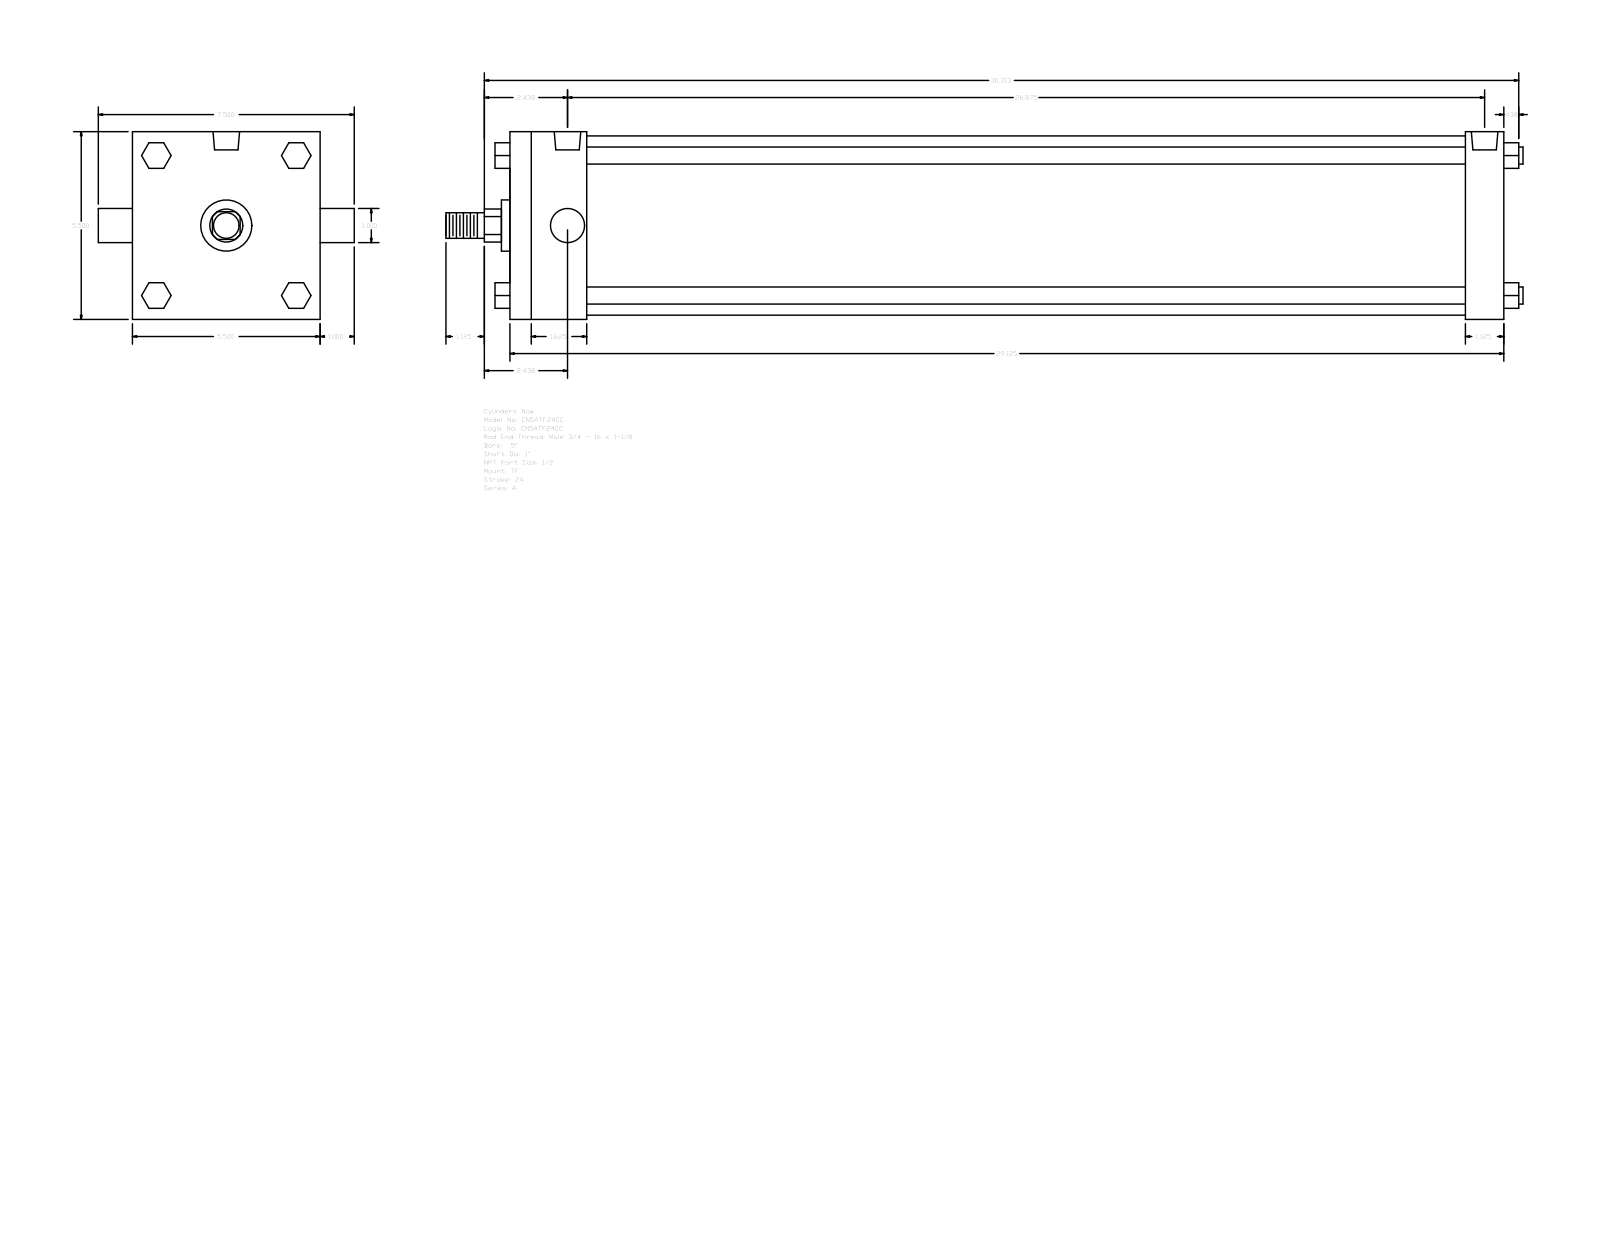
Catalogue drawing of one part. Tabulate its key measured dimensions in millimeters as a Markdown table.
| quantity | value |
| --- | --- |
| part name | A_TF__0500_1 |
| STEP written by | GSSL Pune (CONFIG_CONTROL_DESIGN) |
| units | millimeters |
| bodies | 0 solids, 120 faces (92 planar, 28 cylindrical, 0 other) |
| overall size | 801.69 × 190.5 × 139.7 |
| round holes (diameter × count) | 8.73 × 3, 19.77 × 2 |
| round bosses / shafts (diameter × count) | 12.7 × 4, 25.4 × 2, 133.35 × 1, 38.1 × 1, 19.05 × 1 |
| partial cylindrical surfaces (radius × count) | 12.29 × 1 |
| main face-to-face distances | 139.7, 739.78, 711.2, 28.58, 57.15, 654.05, 682.63, 19.05, 52.07, 90.18 |
| hole center spacings | 2.39, 680.24, 677.85, 682.63 |
